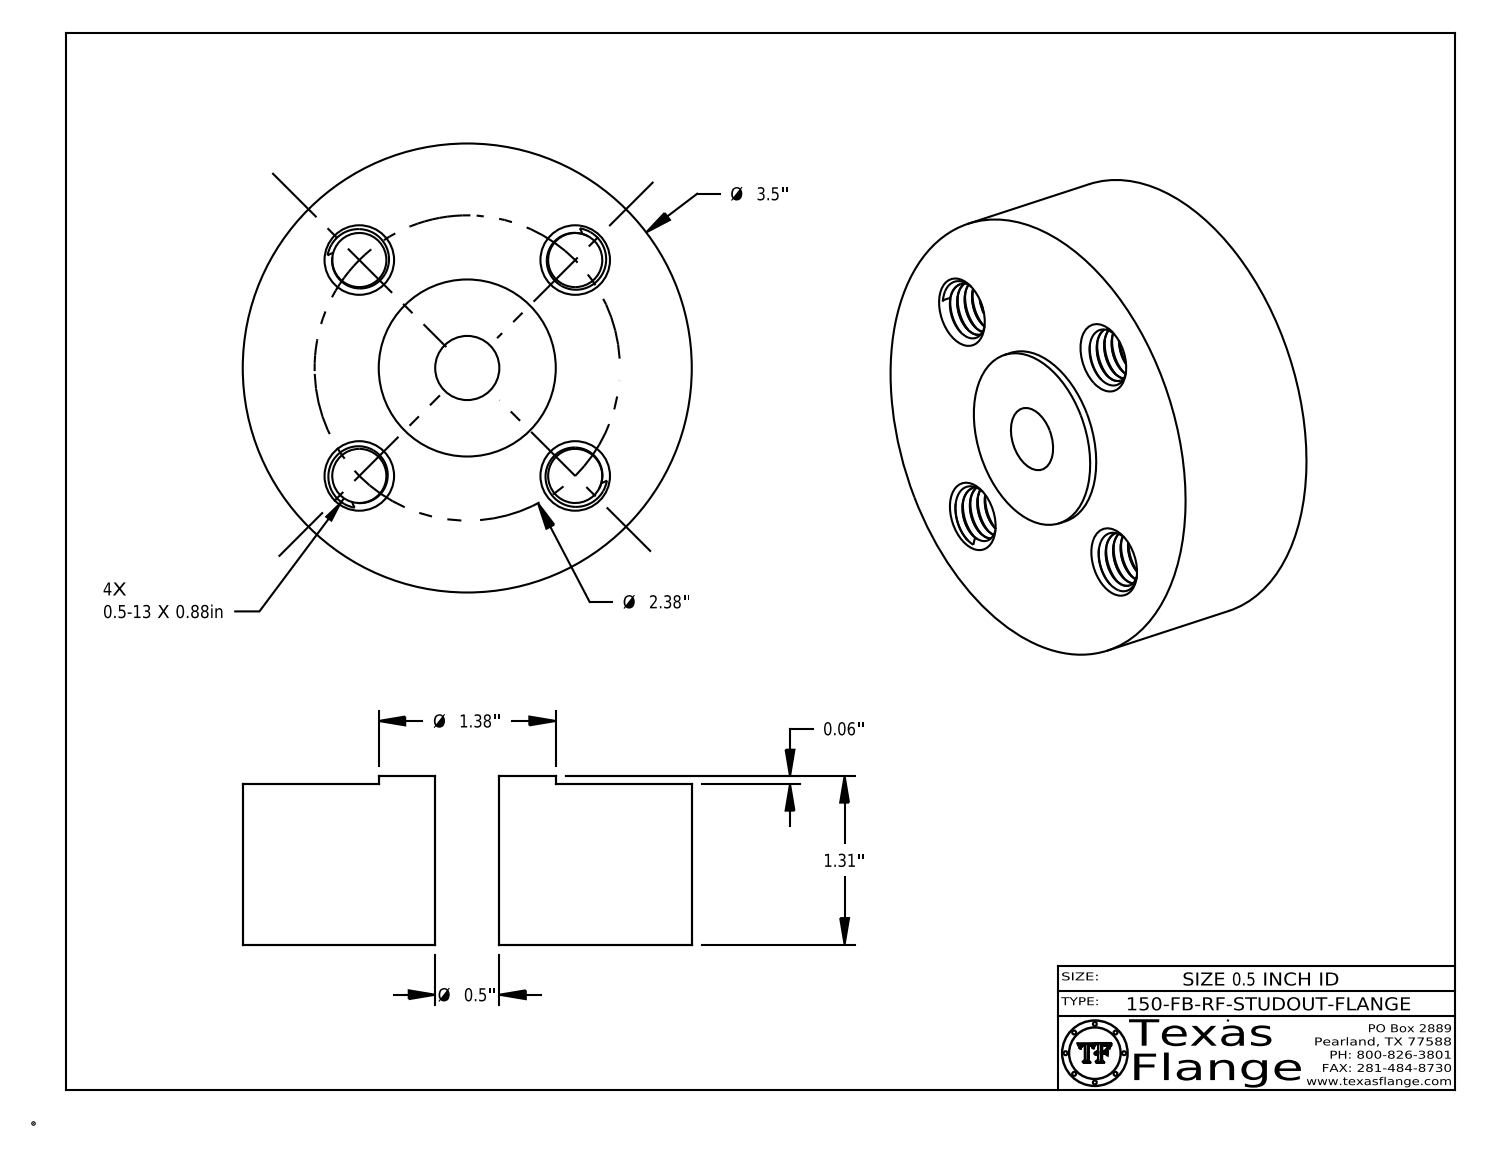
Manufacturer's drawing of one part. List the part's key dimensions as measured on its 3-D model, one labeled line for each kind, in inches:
Part name (STEP PRODUCT): 0.5-150-FB-RF-STUDOUT-FLANGE
STEP written by: CATIA V5 STEP AP214 (AUTOMOTIVE_DESIGN)
Units: inches
Bodies: 1 solid, 586 faces (368 planar, 82 cylindrical, 136 other)
Overall size (bounding box): 3.5 × 3.5 × 1.313
Volume: 11.28 in³ · Surface area: 41.11 in²
Round holes (diameter × count): ⌀0.422 ×4, ⌀0.5 ×1, ⌀1 ×1
Round bosses / shafts (diameter × count): ⌀0.061 ×8, ⌀3.5 ×1, ⌀1.38 ×1, ⌀0.788 ×1
Main face-to-face distances: 1.25, 0.063, 1.313, 0.015, 1.298, 1.235, 0.298, 0.292, 0.054, 0.248
Hole centre spacings: 1.19, 1.683, 0.911, 2.199, 2.38, 1.19
